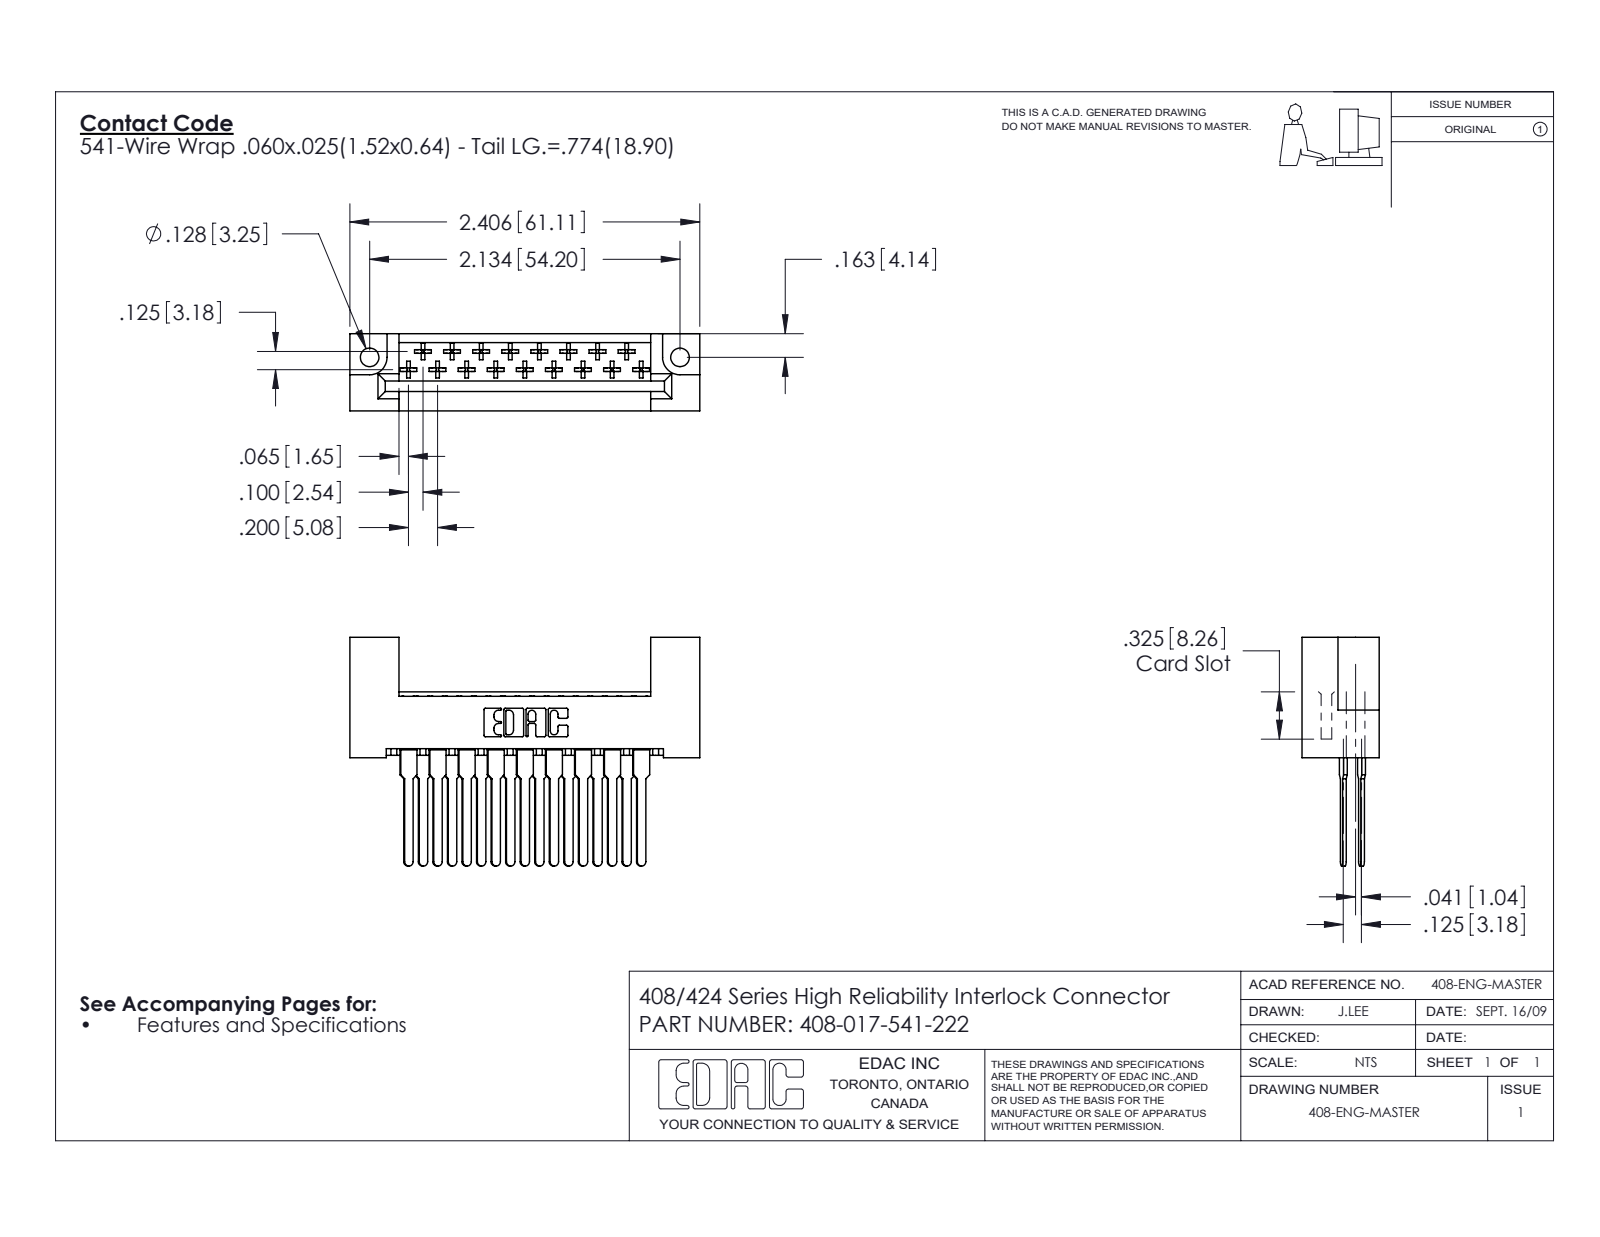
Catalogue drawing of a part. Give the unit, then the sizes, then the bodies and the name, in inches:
Units: inches
Overall size (bounding box): 2.406 × 1.572 × 0.531
Round holes (diameter × count): ⌀0.128 ×2
Partial cylindrical surfaces — rounded edges, fillets, slot ends (radius × count): R0.01 ×102, R0.01 ×22, R0.02 ×19, R0.03 ×17, R0.007 ×6, R0.031 ×6, R0.026 ×3, R0.12 ×2
Main face-to-face distances: 0.531, 0.025, 0.125, 0.025, 0.1, 0.104, 0.095, 0.133, 0.361, 0.326
Hole centre spacings: 2.134
Volume: 0.522 in³ · Surface area: 15.53 in²
Bodies: 18 solids, 1040 faces (769 planar, 203 cylindrical, 68 other)
Part name (STEP PRODUCT): 408-017-541-222; 408-290-001_408-290-141; 408 Part_017 - 2
STEP written by: SolidWorks 2016 (CONFIG_CONTROL_DESIGN)
